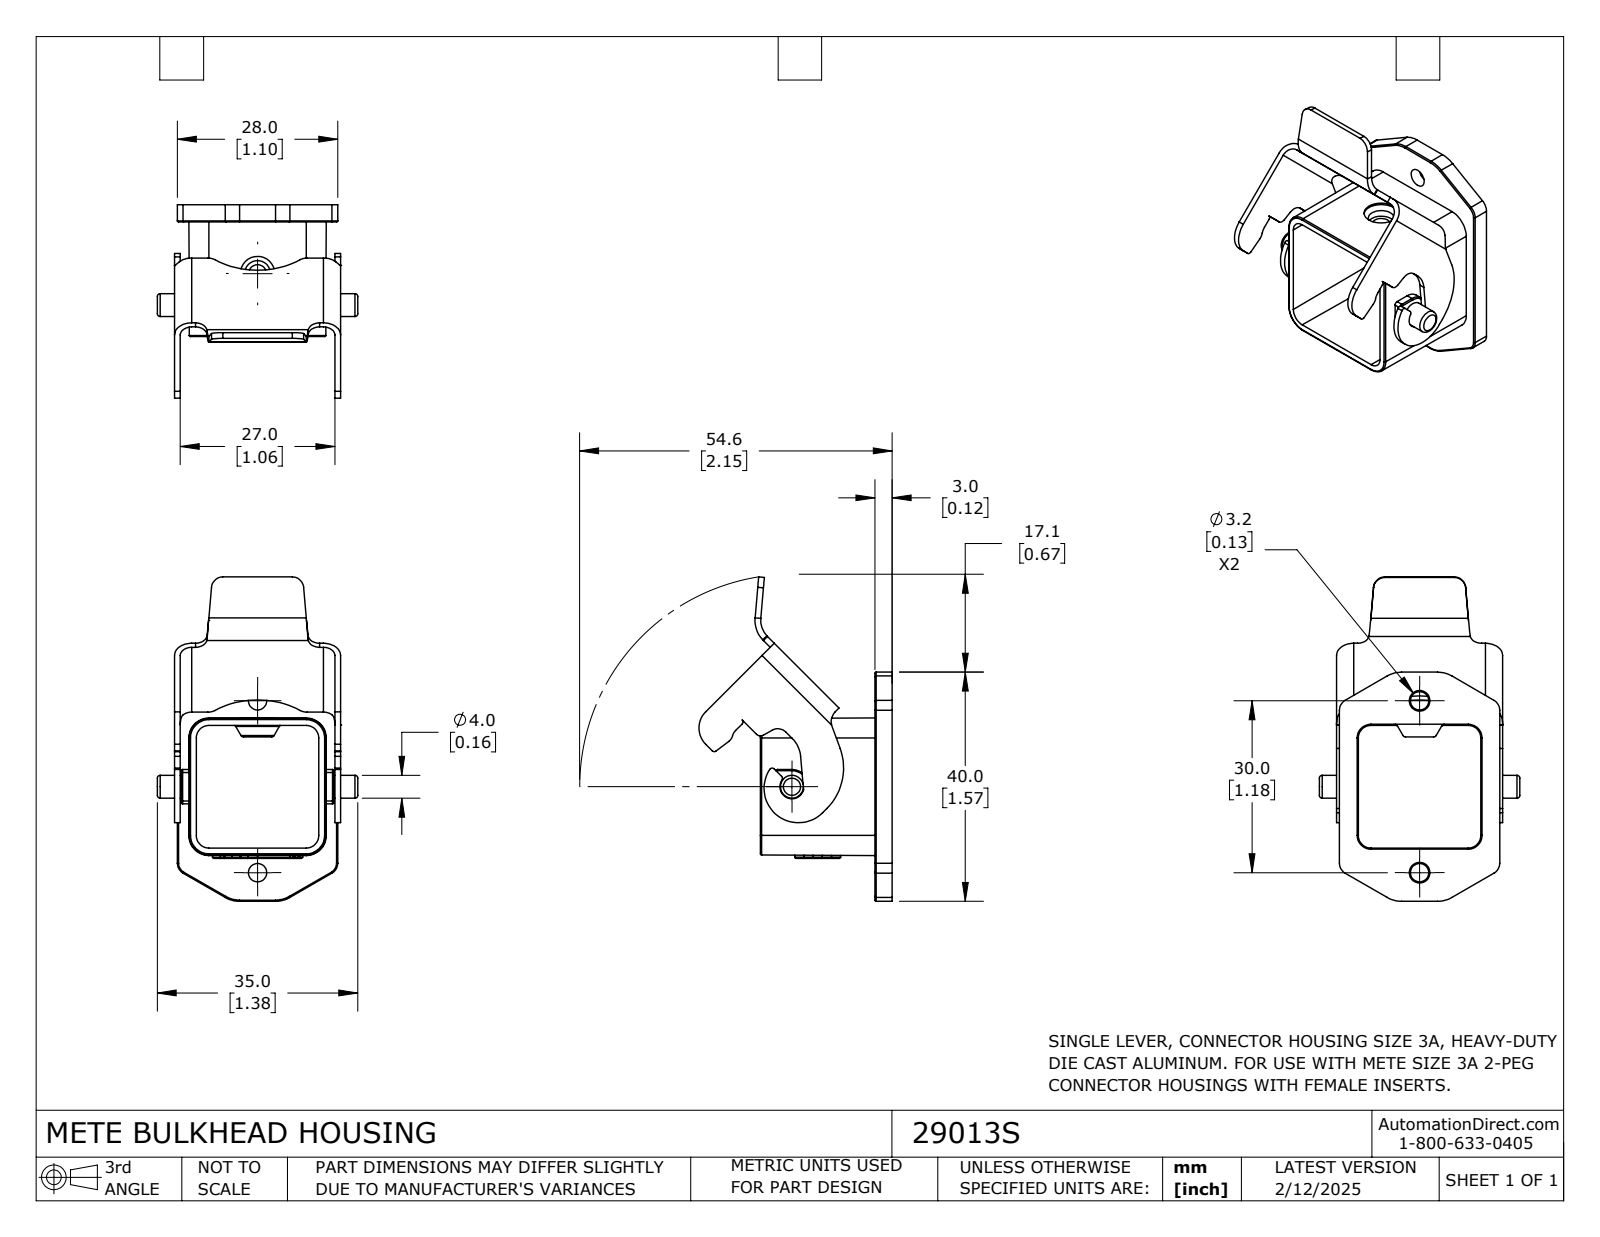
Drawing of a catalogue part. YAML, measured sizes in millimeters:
part_name: "29013S"
step_written_by: "SolidWorks 2024 (CONFIG_CONTROL_DESIGN)"
units: millimeters
bodies: {solids: 1, faces: 285, planar: 110, cylindrical: 130, other: 45}
overall_size: [56.6, 35, 33.7]
volume: 5280
surface_area: 8329
round_holes:
  - {diameter: 3.2, count: 2}
  - {diameter: 3.6, count: 2}
  - {diameter: 3.1, count: 1}
  - {diameter: 4.5, count: 1}
  - {diameter: 6, count: 1}
round_bosses_or_shafts:
  - {diameter: 4, count: 1}
partial_cylinders:
  - {radius: 0.2, count: 35}
  - {radius: 2, count: 13}
  - {radius: 0.5, count: 10}
  - {radius: 5, count: 6}
  - {radius: 2.4, count: 4}
  - {radius: 3, count: 3}
  - {radius: 2.1, count: 2}
  - {radius: 4, count: 2}
face_to_face_distances: [1, 28, 3, 27, 29, 0.5, 28.5, 27.5, 23, 20]
hole_center_spacings: [30]
